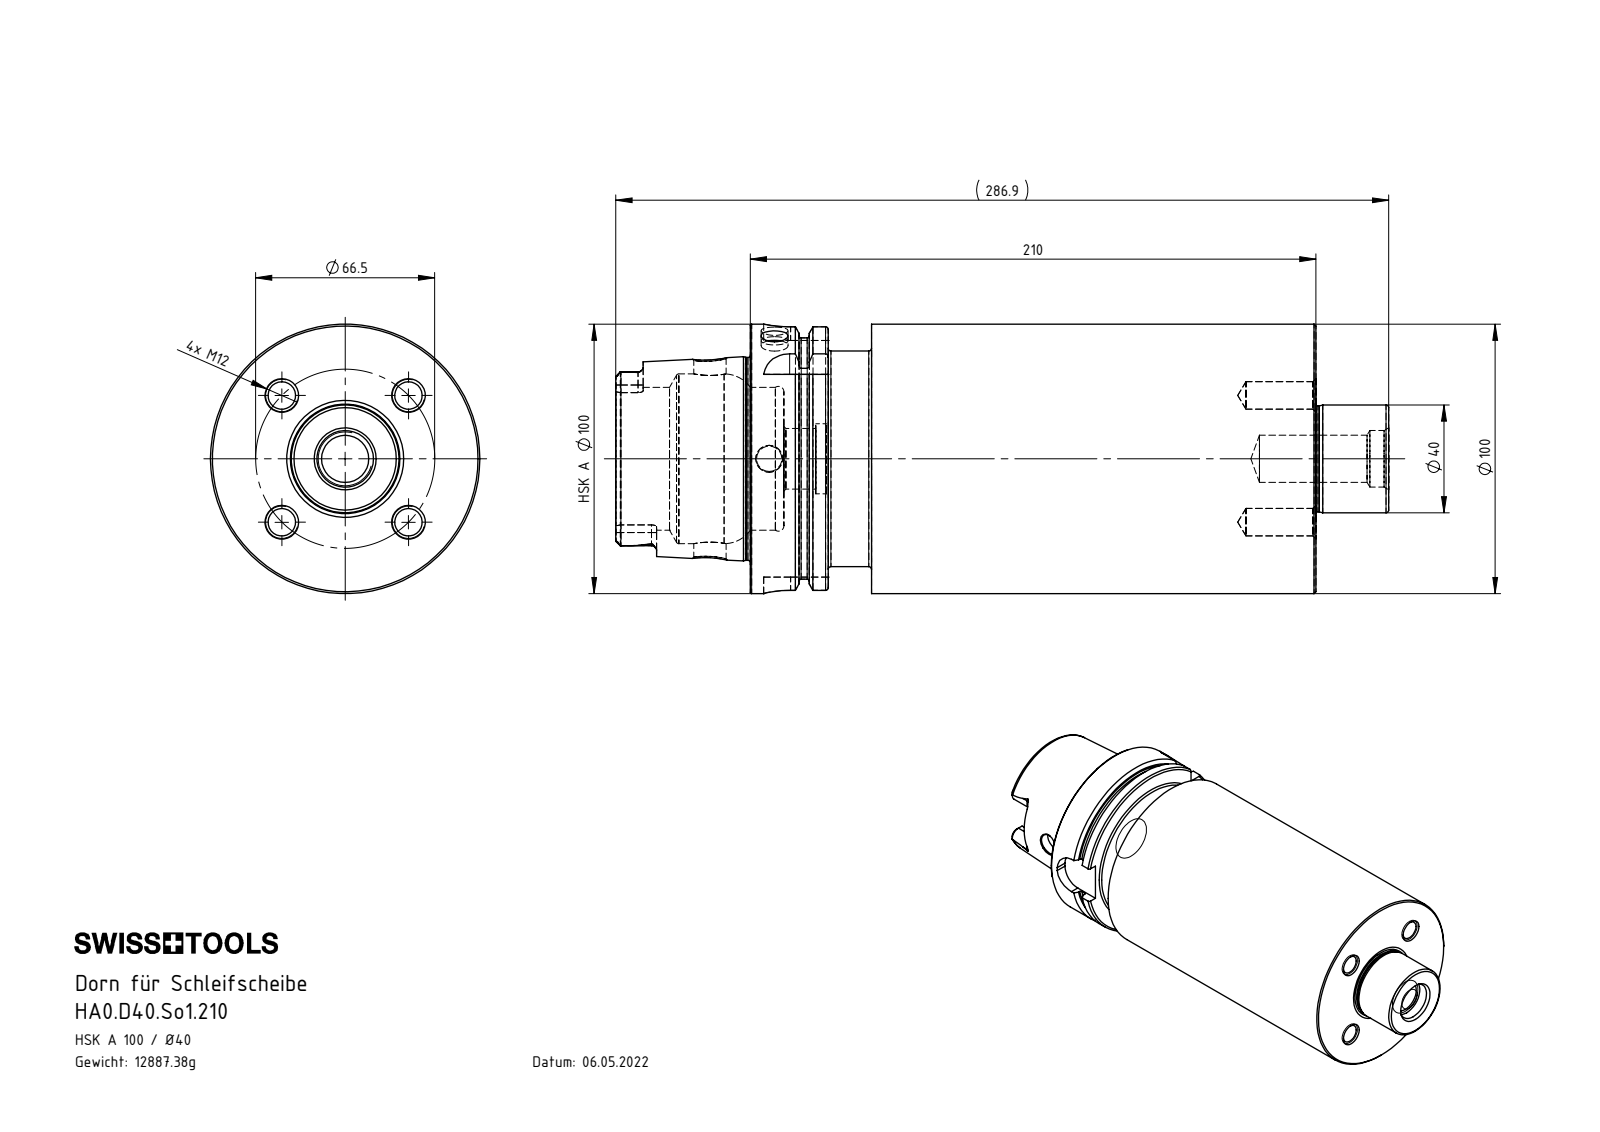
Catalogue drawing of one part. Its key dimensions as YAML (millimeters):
part_name: "0-D.0.So1.210_A"
step_written_by: "SolidWorks 2017 (AUTOMOTIVE_DESIGN)"
units: millimeters
bodies: {solids: 1, faces: 231, planar: 44, cylindrical: 74, other: 113}
overall_size: [286.9, 100, 100]
volume: 1641000
surface_area: 121255
round_holes:
  - {diameter: 5, count: 4}
  - {diameter: 10.2, count: 4}
  - {diameter: 10, count: 3}
  - {diameter: 12, count: 1}
  - {diameter: 17.5, count: 1}
  - {diameter: 21, count: 1}
  - {diameter: 22.5, count: 1}
  - {diameter: 26, count: 1}
  - {diameter: 53, count: 1}
  - {diameter: 63, count: 1}
round_bosses_or_shafts:
  - {diameter: 100, count: 1}
  - {diameter: 91.95, count: 1}
  - {diameter: 80, count: 1}
  - {diameter: 75.26, count: 1}
  - {diameter: 40, count: 1}
  - {diameter: 39.3, count: 1}
partial_cylinders:
  - {radius: 1.9, count: 6}
  - {radius: 4.88, count: 4}
  - {radius: 10, count: 4}
face_to_face_distances: [210, 45, 165, 28.95, 16.05, 181.05, 12.45, 16.5, 32.55, 197.55]
hole_center_spacings: [33.25, 47.02, 66.5]
